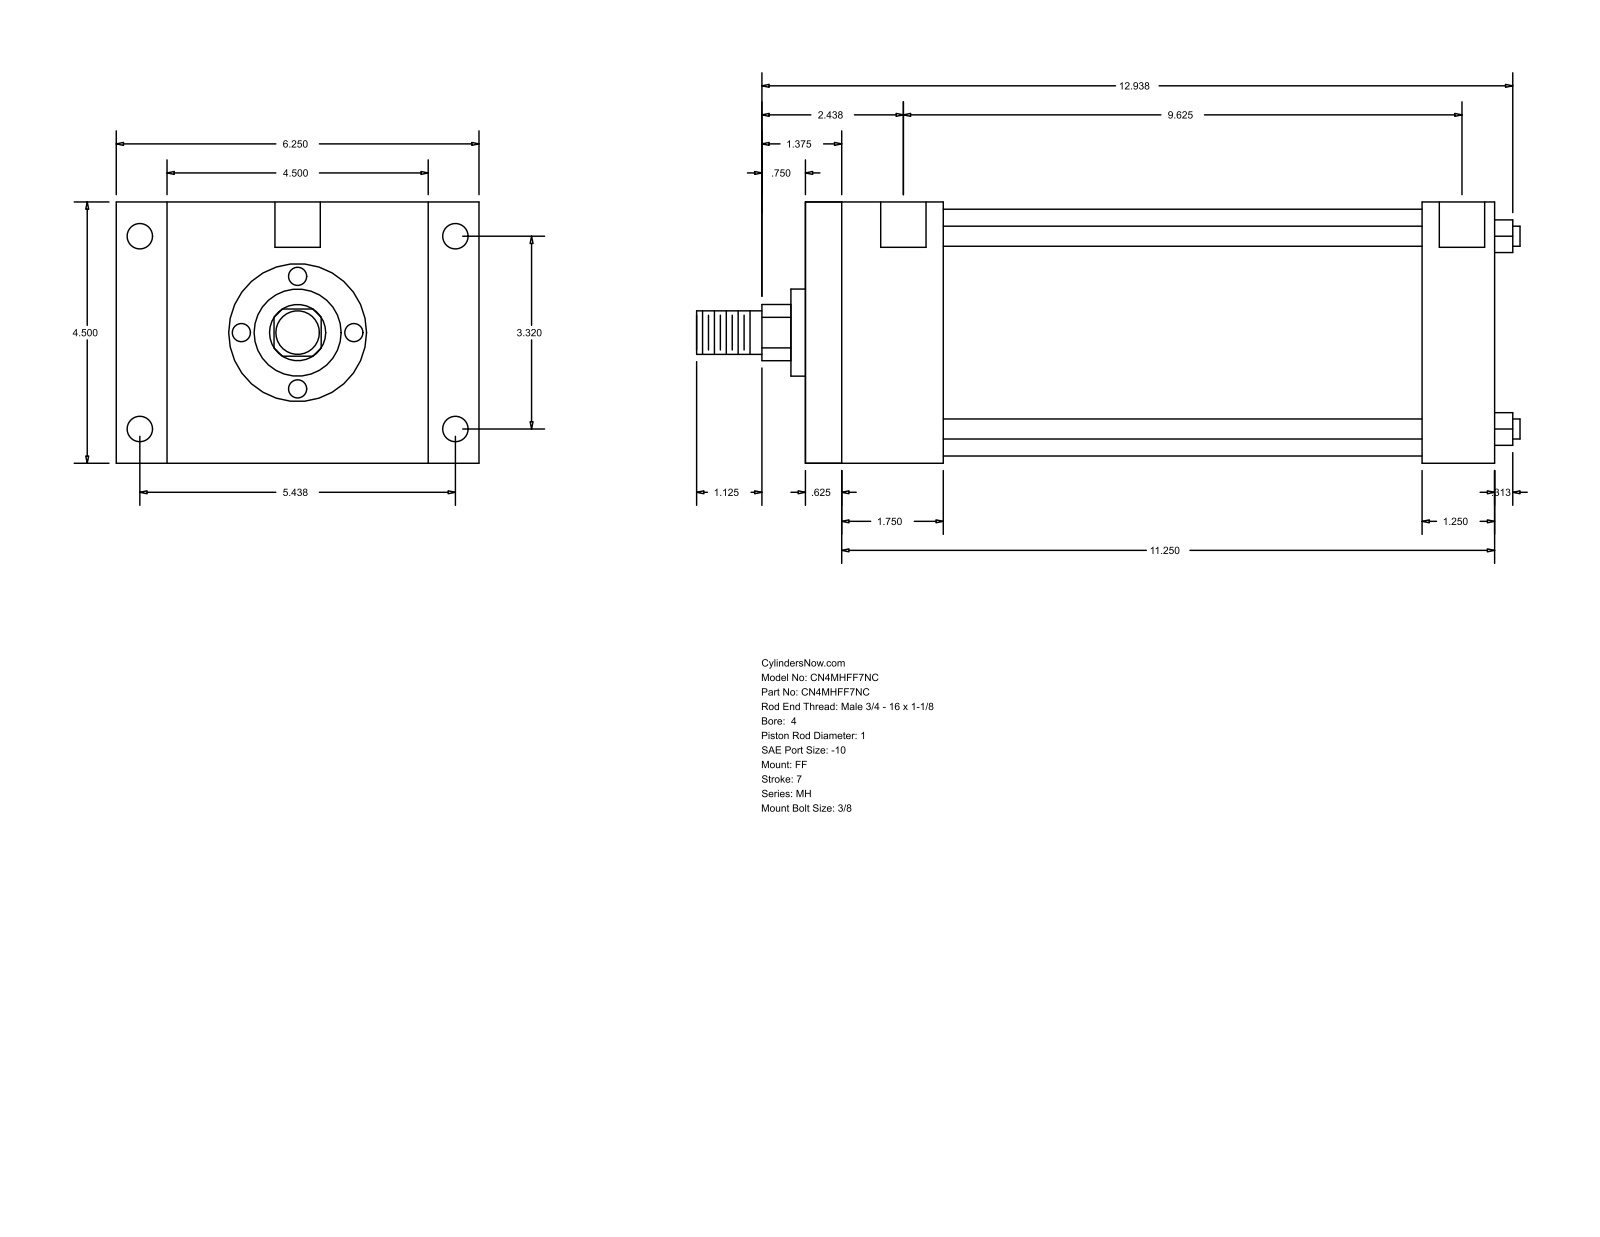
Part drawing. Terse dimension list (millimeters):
name: MH_FF__0400_1
written by: GSSL Pune (CONFIG_CONTROL_DESIGN)
unit: mm
bodies: 0 solids, 92 faces (64 planar, 28 cylindrical, 0 other)
size: 360.36 × 158.75 × 114.3
holes: 4× ⌀8.73, 4× ⌀11.13, 2× ⌀19.84
bosses: 4× ⌀8.76, 1× ⌀107.95, 1× ⌀38.1, 1× ⌀25.4, 1× ⌀19.05
rounds: 1× R12.29
face distances: 114.3, 301.63, 15.87, 285.76, 60.33, 44.46, 241.3, 269.88, 254.01, 209.55
hole spacings: 84.32, 138.12, 161.82, 247.65, 1.58, 1.59, 244.48, 246.06
